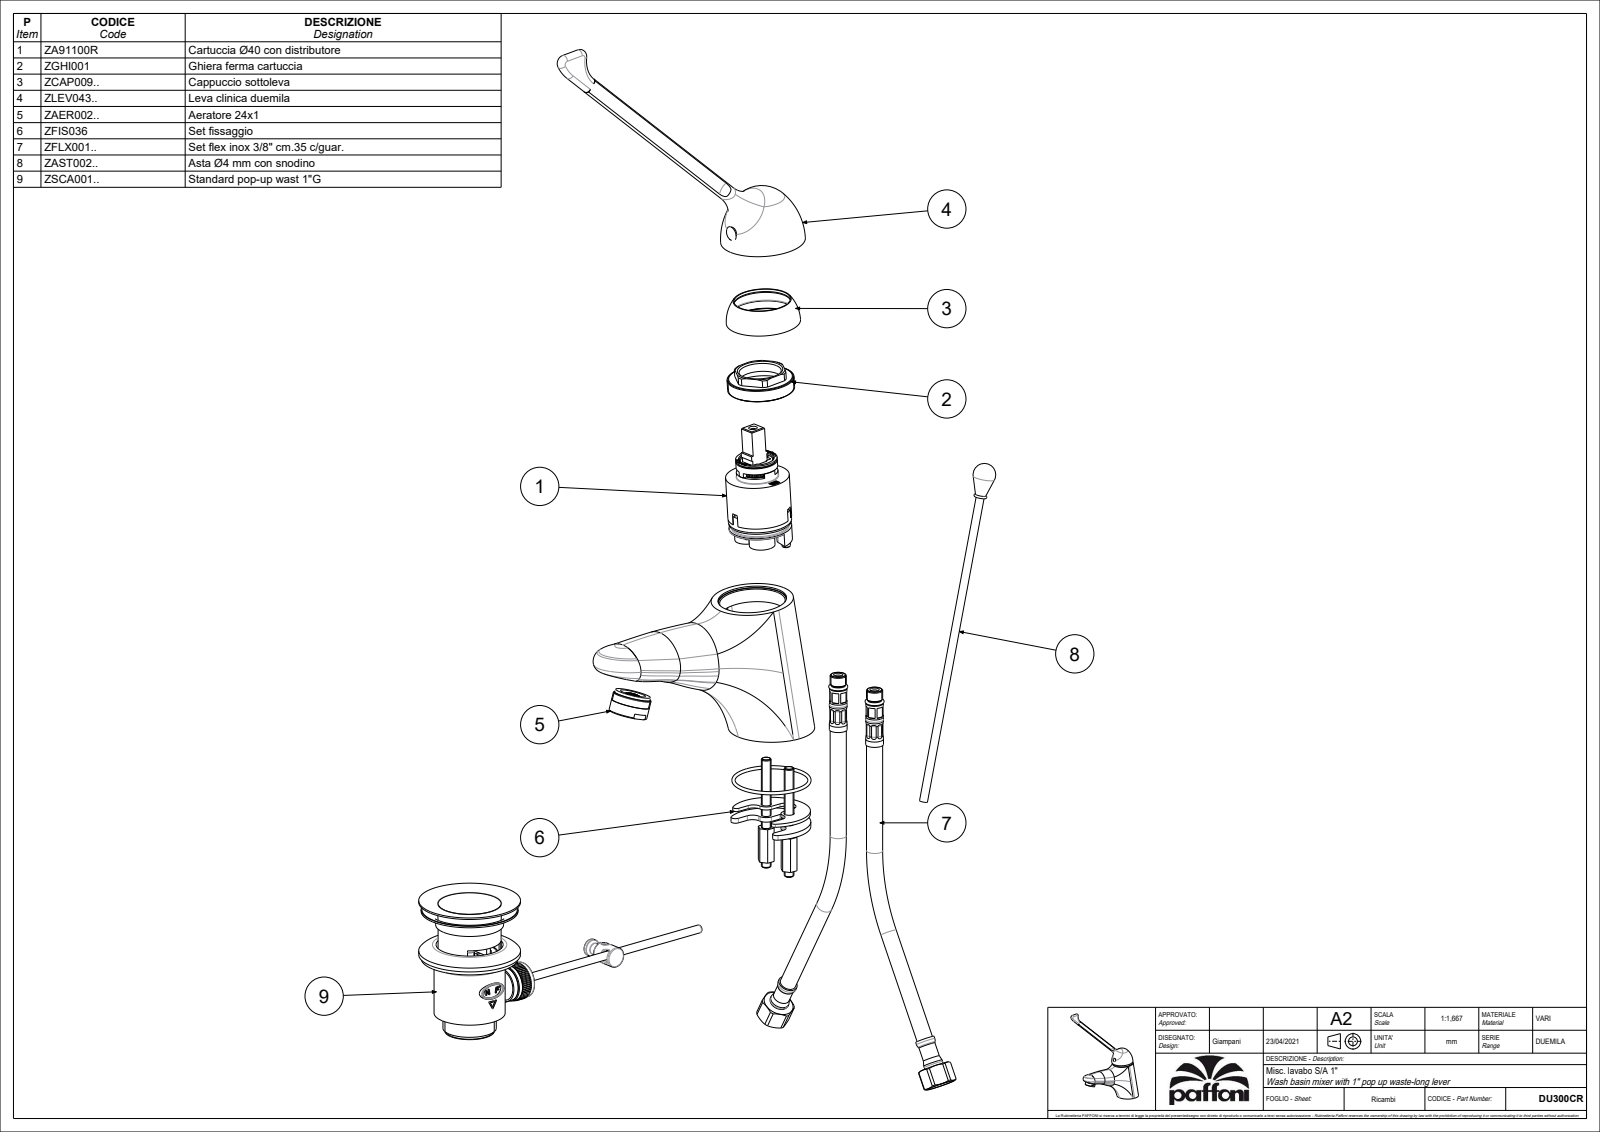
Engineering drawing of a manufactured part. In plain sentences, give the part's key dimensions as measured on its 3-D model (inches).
The part is named "DU300CR". Its 3-D file was written by "CREO PARAMETRIC BY PTC INC, 2020044 (CONFIG_CONTROL_DESIGN)". It is 3 solids with 263 faces: 54 planar, 72 cylindrical and 137 other. Overall it measures 9.997 by 8.563 by 2.106 inches. Its volume is 17.55 cubic inches and its surface area 104.6 square inches. Round holes: 4 of diameter 0.217, 2 of diameter 0.207, 2 of diameter 0.276, 2 of diameter 0.315, 2 of diameter 0.354, 2 of diameter 0.433, 1 of diameter 0.197, 1 of diameter 0.236, 1 of diameter 0.965, 1 of diameter 1.378, 1 of diameter 1.539, 1 of diameter 1.594. Round bosses or shafts: 1 of diameter 1.752, 1 of diameter 0.945, 1 of diameter 0.394, 1 of diameter 0.315, 1 of diameter 0.197. Partial cylindrical surfaces (rounded edges, fillets, slot ends): 2 of radius 0.118, 1 of radius 0.157, 1 of radius 0.62. The main face-to-face distances are 0.236, 2.028, 2.03, 0.189, 0.425, 0.315, 0.079, 0.11, 0.504, 0.394. The hole center spacings are 0.339, 0.615, 0.432, 0.476, 0.53, 0.591, 0.622, 0.89.
